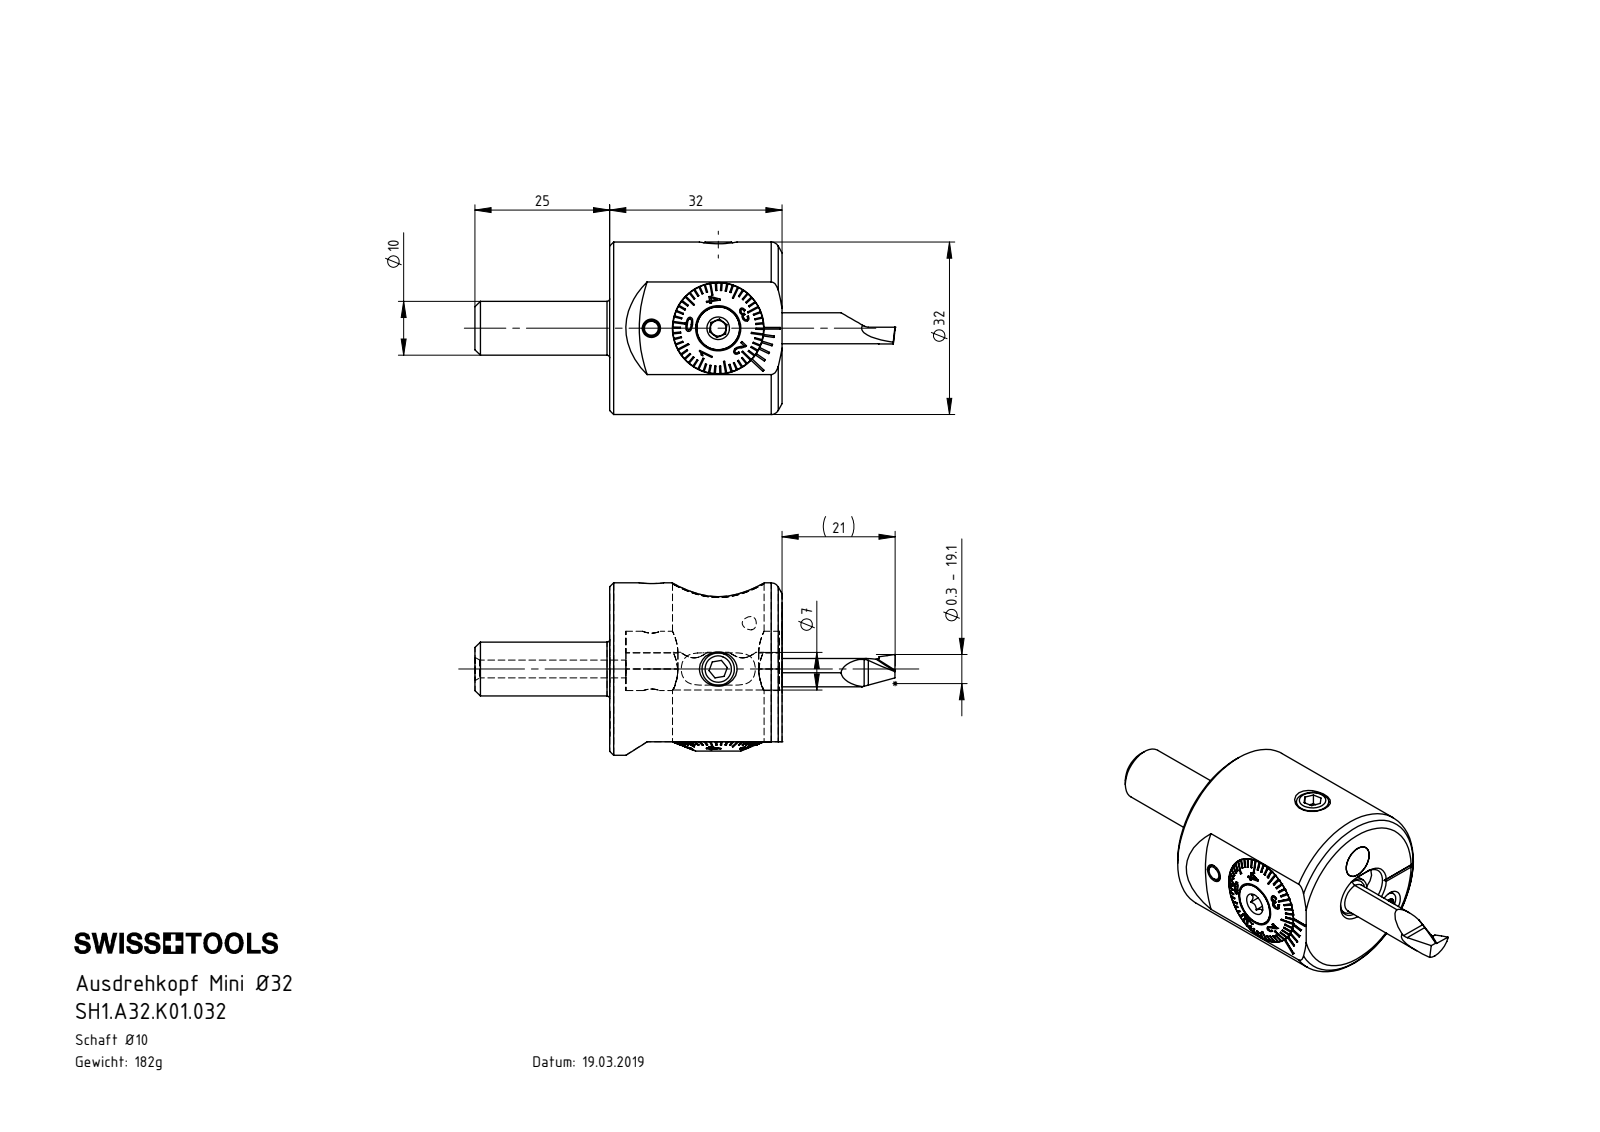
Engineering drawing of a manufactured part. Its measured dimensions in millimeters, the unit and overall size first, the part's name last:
Units: millimetres
Overall size (bounding box): 57 × 32 × 32
Round holes (diameter × count): ⌀5 ×7, ⌀3.3 ×3, ⌀1 ×1, ⌀2 ×1, ⌀2.5 ×1, ⌀2.9 ×1, ⌀3 ×1, ⌀6 ×1, ⌀7 ×1, ⌀7.75 ×1, ⌀8.4 ×1, ⌀10.2 ×1
Round bosses / shafts (diameter × count): ⌀6 ×3, ⌀10 ×2, ⌀32 ×1, ⌀17 ×1, ⌀16.98 ×1, ⌀16.85 ×1, ⌀14.65 ×1, ⌀8 ×1
Partial cylindrical surfaces — rounded edges, fillets, slot ends (radius × count): R0.21 ×6, R0.36 ×5, R0.2 ×4, R2.2 ×4, R4 ×2, R0.36 ×1, R0.5 ×1, R1.9 ×1
Main face-to-face distances: 32, 4.5, 3.7, 0.8, 1.5, 2.3, 2.2, 3, 4.6, 4.4
Hole centre spacings: 4.5, 10.4, 11.88, 12.21, 0.4, 7.9, 8, 8.01
Volume: 23 630 mm³ · Surface area: 14 219 mm²
Bodies: 15 solids, 707 faces (302 planar, 135 cylindrical, 270 other)
Part name (STEP PRODUCT): A32-BG1.012.017; A32-BG2.014.010_A; SH1-A32.K01.032_B; F32-BG2.017.003_A (+8 more)
STEP written by: SolidWorks 2022 (AUTOMOTIVE_DESIGN)
